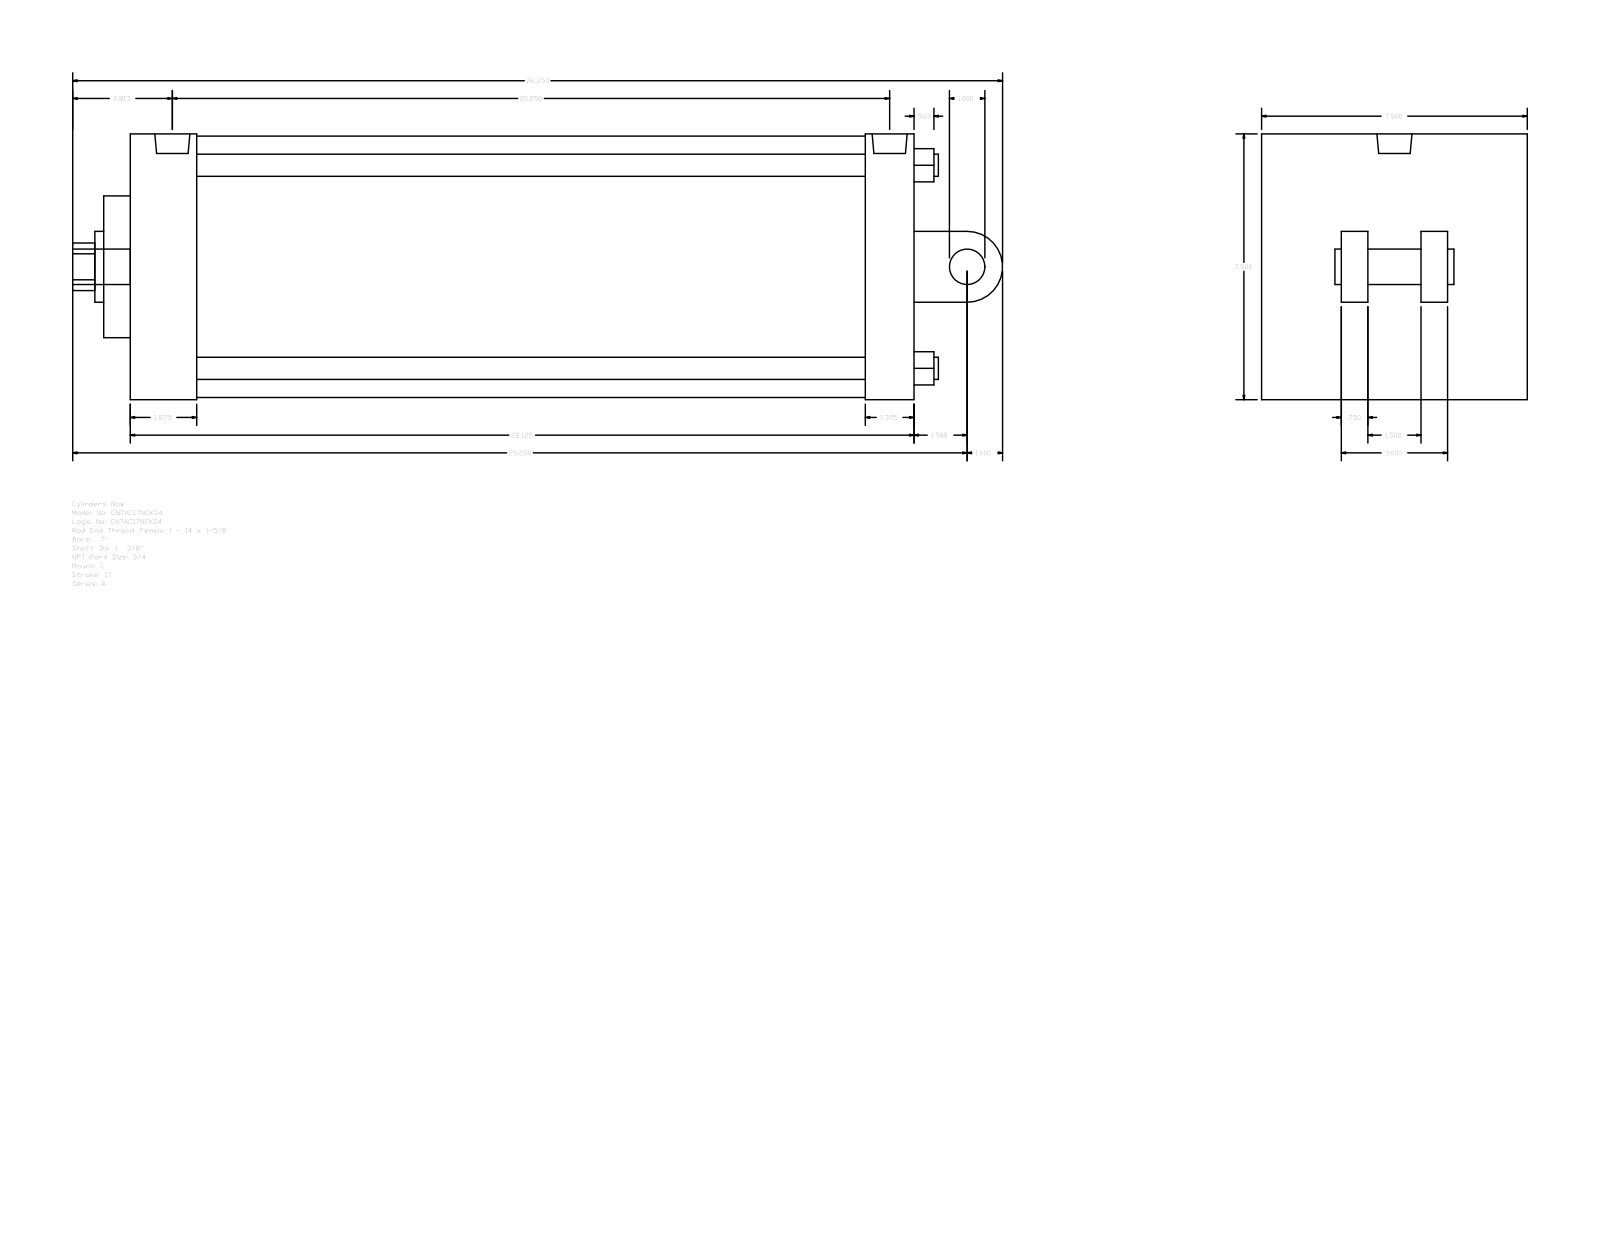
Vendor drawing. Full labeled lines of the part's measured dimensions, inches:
Part name (STEP PRODUCT): A_C__0700_1.375
STEP written by: GSSL Pune (CONFIG_CONTROL_DESIGN)
Units: inches
Bodies: 0 solids, 104 faces (75 planar, 29 cylindrical, 0 other)
Overall size (bounding box): 26.25 × 7.5 × 7.5
Round holes (diameter × count): ⌀0.625 ×4, ⌀0.594 ×2, ⌀0.989 ×1, ⌀1.375 ×1, ⌀2 ×1, ⌀7.375 ×1
Round bosses / shafts (diameter × count): ⌀1 ×2, ⌀0.594 ×2, ⌀0.989 ×1
Partial cylindrical surfaces — rounded edges, fillets, slot ends (radius × count): R0.672 ×1, R1 ×1
Main face-to-face distances: 7.5, 22.125, 3, 2.25, 0.75, 22.875, 2.625, 1.875, 20.25, 21.5
Hole centre spacings: 4.052, 5.73, 8.103, 0.219
